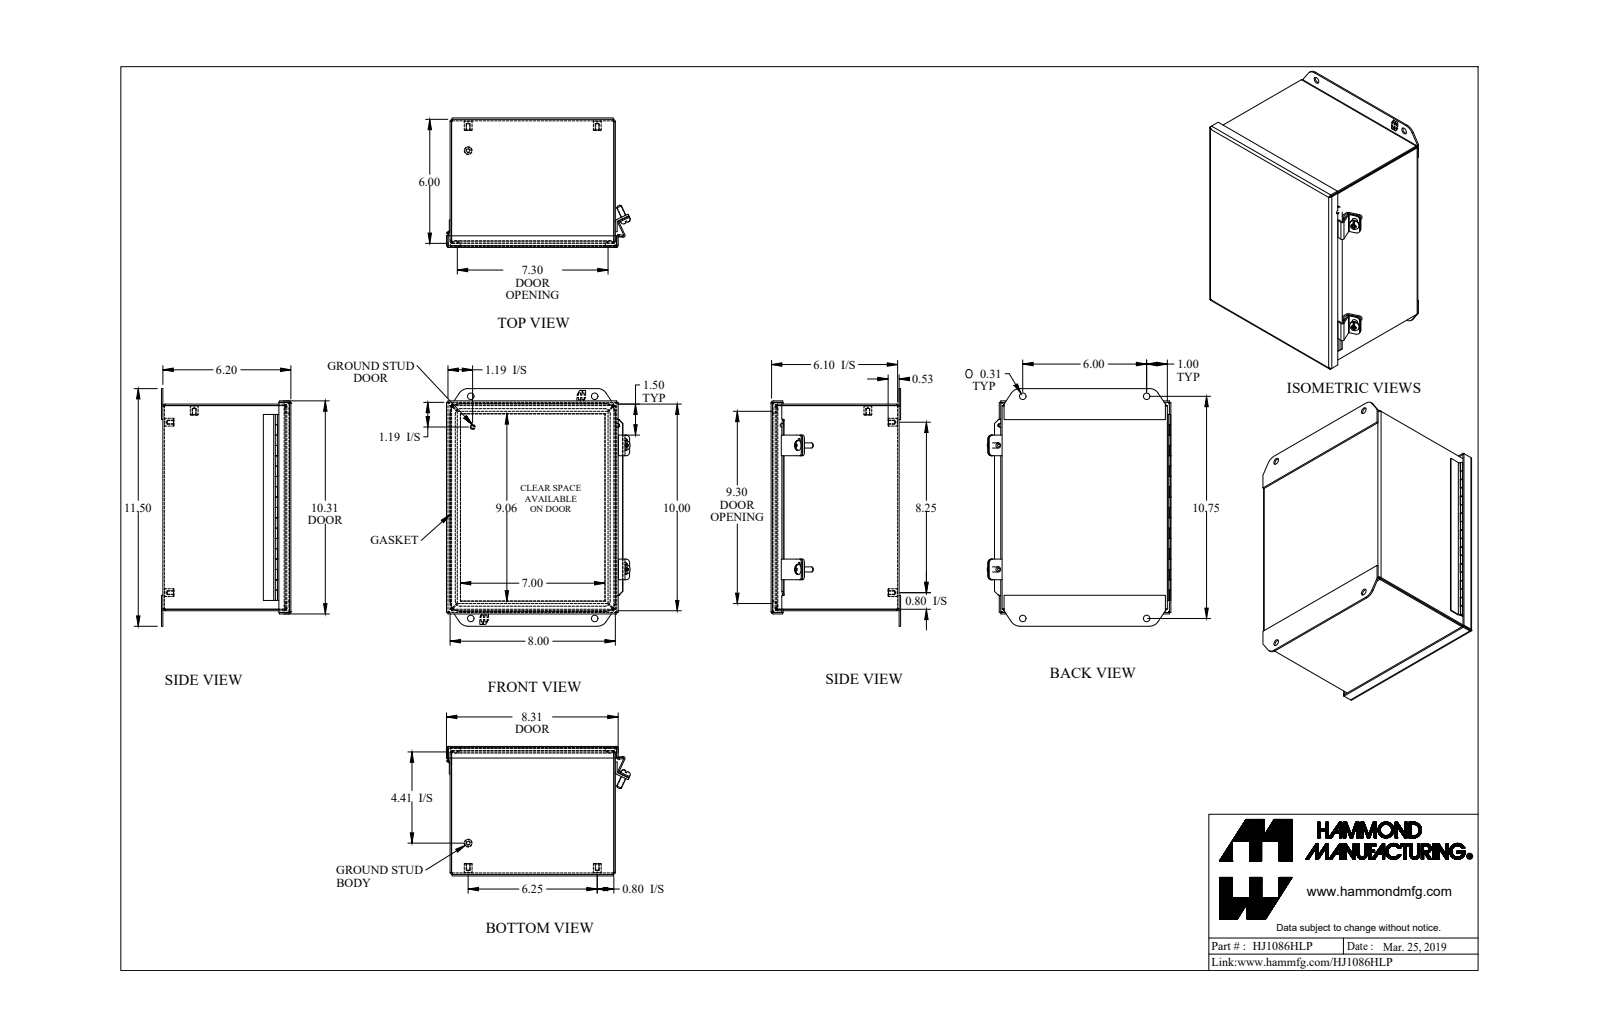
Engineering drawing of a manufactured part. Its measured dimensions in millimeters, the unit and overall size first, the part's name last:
Units: millimetres
Overall size (bounding box): 292.1 × 226 × 159.2
Round holes (diameter × count): ⌀4 ×5, ⌀8 ×4, ⌀5.4 ×2, ⌀1.3 ×1
Round bosses / shafts (diameter × count): ⌀9.5 ×5, ⌀6.4 ×3, ⌀12.2 ×2, ⌀4.8 ×1, ⌀2.5 ×1, ⌀1.1 ×1
Partial cylindrical surfaces — rounded edges, fillets, slot ends (radius × count): R6.4 ×16, R0.9 ×13, R2.7 ×13, R4.8 ×8, R0.3 ×4, R3.6 ×4, R12.7 ×4, R12.7 ×4
Main face-to-face distances: 1.8, 155.6, 201.4, 157.4, 252.2, 153.7, 203.2, 199.5, 254, 250.3
Hole centre spacings: 31.9, 241.3, 152.4, 158.8, 287.1, 209.6, 262.9, 273.1
Volume: 573 700 mm³ · Surface area: 635 700 mm²
Bodies: 20 solids, 745 faces (398 planar, 219 cylindrical, 128 other)
Part name (STEP PRODUCT): HJ1086HLP
STEP written by: SolidWorks 2018 (AUTOMOTIVE_DESIGN)
